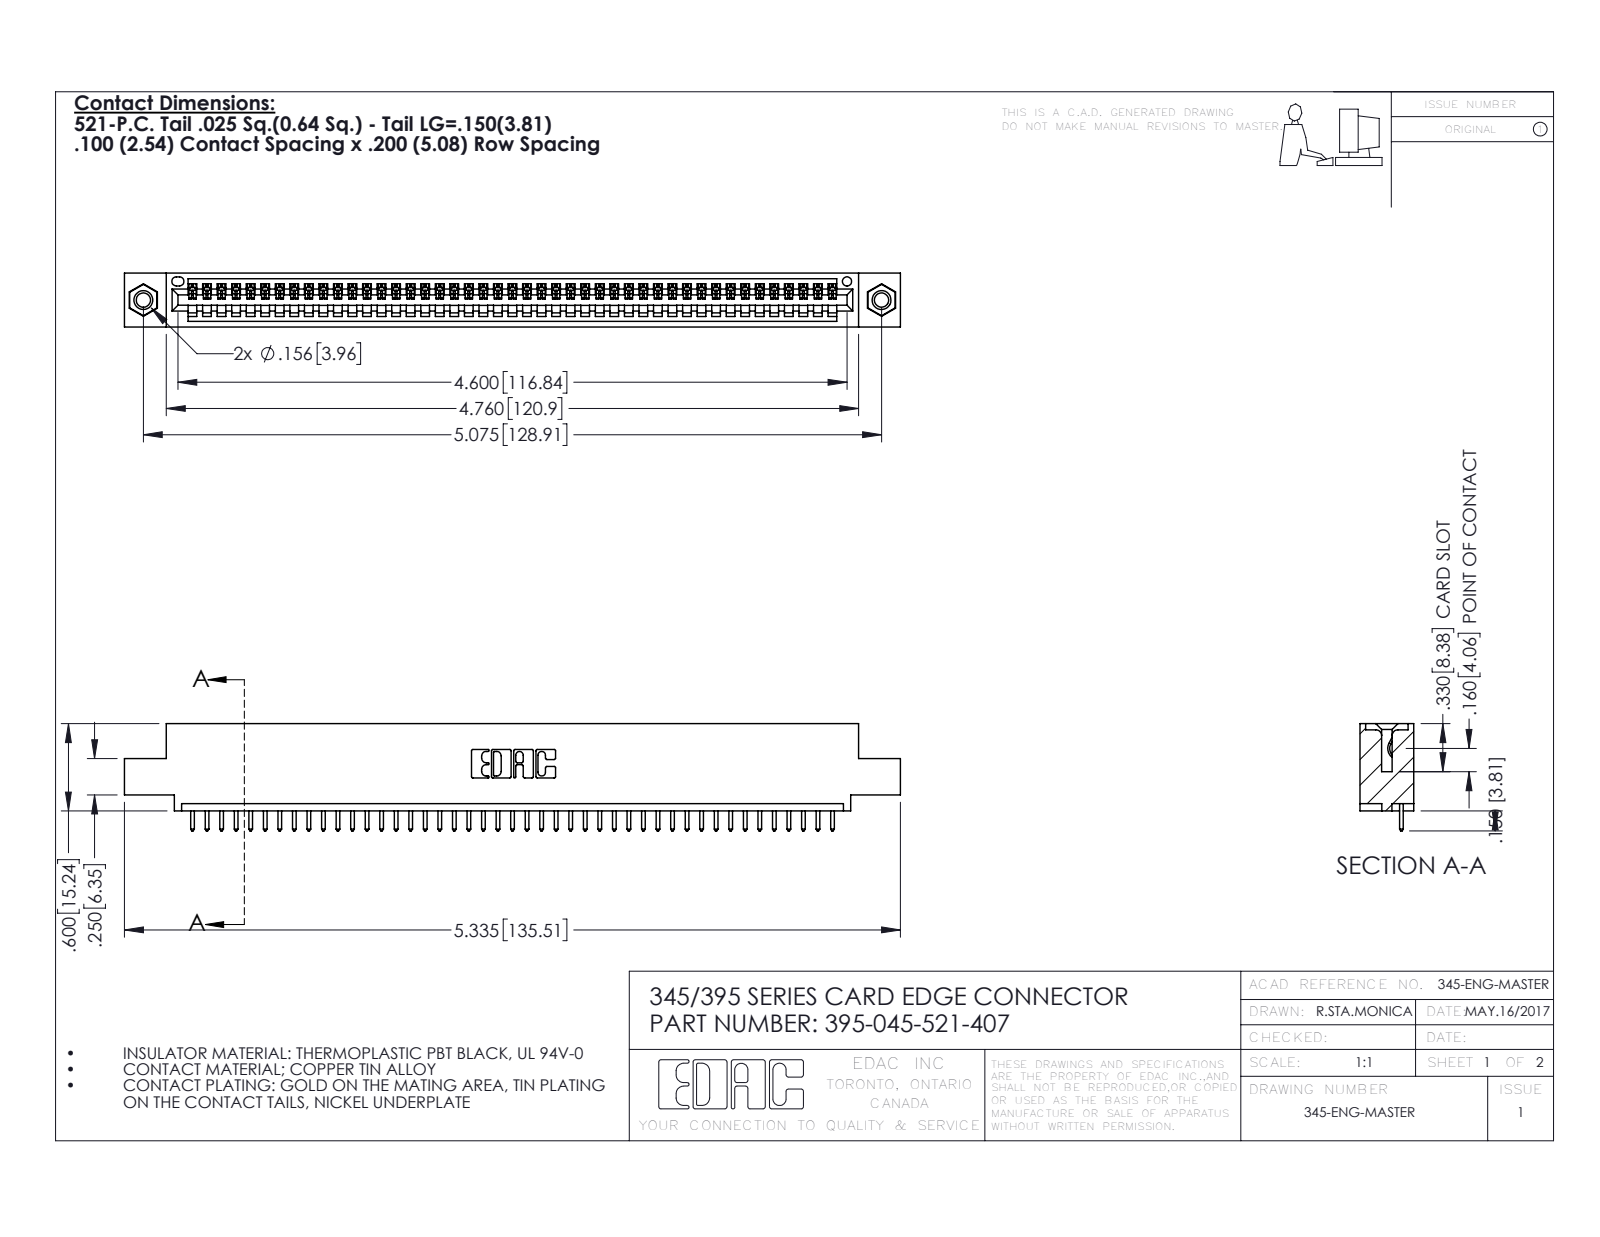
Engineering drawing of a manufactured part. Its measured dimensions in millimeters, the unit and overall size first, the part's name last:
Units: millimetres
Overall size (bounding box): 135.5 × 18.7 × 9.4
Round holes (diameter × count): ⌀2.5 ×2, ⌀3.2 ×2, ⌀4 ×2, ⌀1.6 ×1
Round bosses / shafts (diameter × count): ⌀3.9 ×2
Partial cylindrical surfaces — rounded edges, fillets, slot ends (radius × count): R0.2 ×90, R0.3 ×90, R0.3 ×22, R0.2 ×6, R0.8 ×6, R0.7 ×3, R0.8 ×2, R1 ×2
Main face-to-face distances: 1.8, 7.6, 9.4, 5.1, 2.5, 6.9, 0.6, 5.7, 3.8, 1.8
Hole centre spacings: 6.9, 122.9, 128.9
Volume: 12 700 mm³ · Surface area: 16 500 mm²
Bodies: 48 solids, 2800 faces (1916 planar, 868 cylindrical, 16 other)
Part name (STEP PRODUCT): 395-045-521-407; 345-250-001_345-250-005-103; 345-292-001_345-293-121; 345 Part_0.110 Offset - 0.156 Dia-TI
STEP written by: SolidWorks 2016 (CONFIG_CONTROL_DESIGN)
